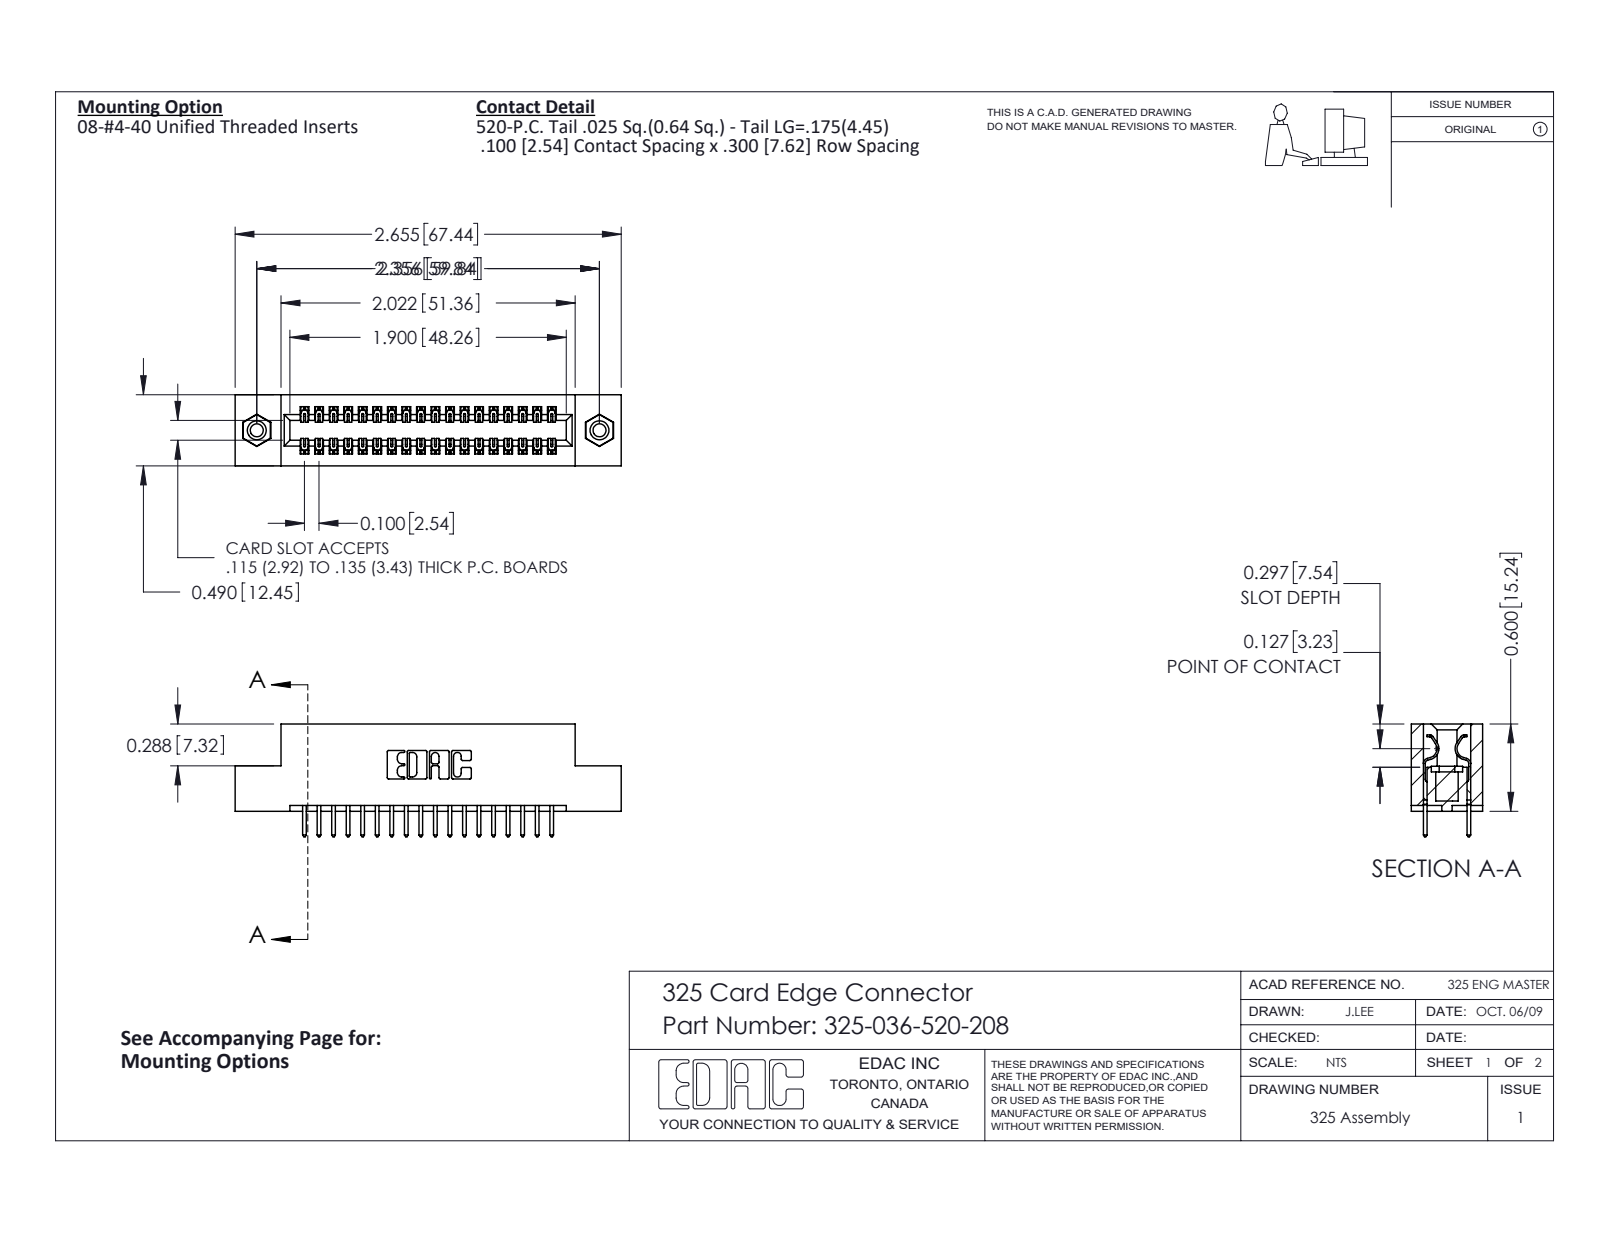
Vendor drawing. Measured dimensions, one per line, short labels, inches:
name: 325-292-001_325-293-120; 345-250-001_345-250-003-102; 325-036-520-208; 325 Part_TI
written by: SolidWorks 2016 (CONFIG_CONTROL_DESIGN)
unit: in
bodies: 39 solids, 2046 faces (1398 planar, 632 cylindrical, 16 other)
size: 2.655 × 0.775 × 0.49
volume: 0.517 in³; area: 14.93 in²
holes: 2× ⌀0.089, 2× ⌀0.125, 2× ⌀0.16
bosses: 2× ⌀0.155
rounds: 54× R0.006, 36× R0.01, 22× R0.01, 6× R0.007, 6× R0.031, 3× R0.026, 2× R0.014, 2× R0.022
face distances: 0.083, 0.407, 0.3, 0.49, 0.107, 0.383, 0.025, 0.325, 0.6, 0.2
hole spacings: 2.356
